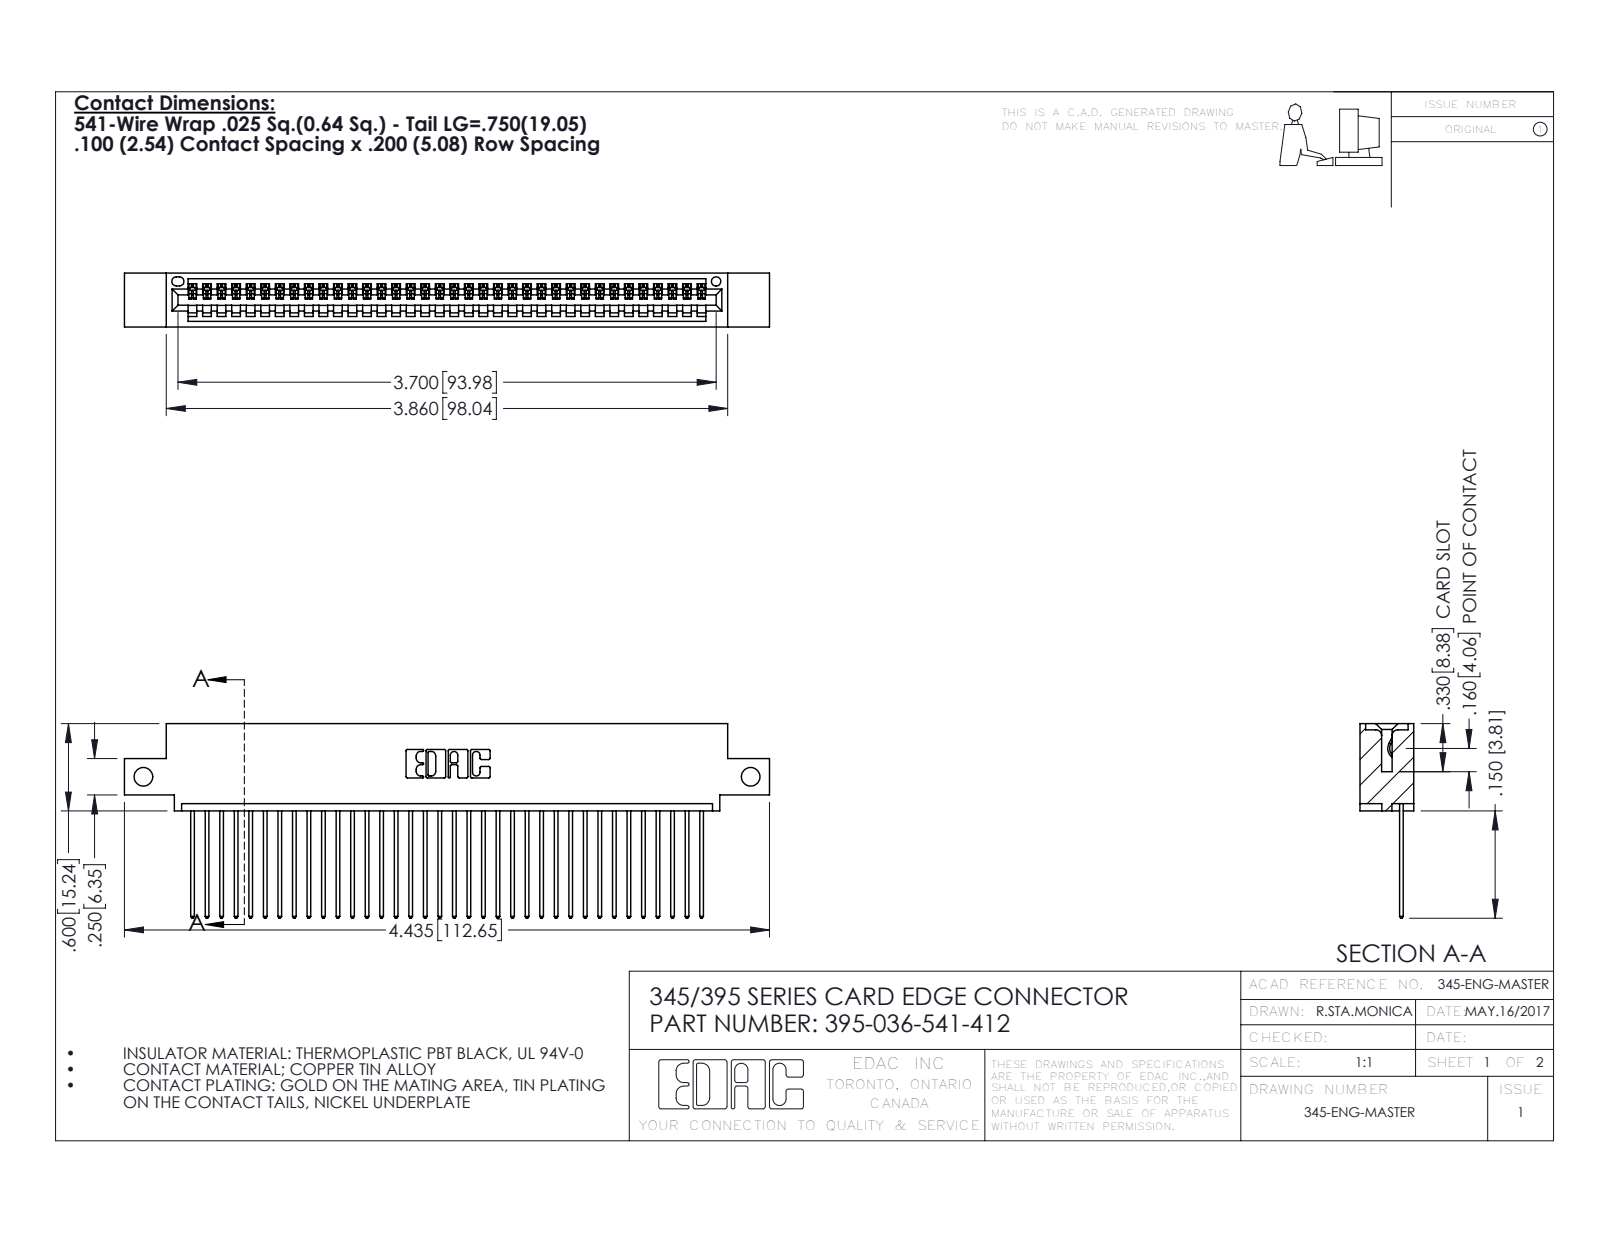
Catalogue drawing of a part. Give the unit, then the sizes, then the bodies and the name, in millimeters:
Units: millimetres
Overall size (bounding box): 112.6 × 34 × 9.4
Round holes (diameter × count): ⌀3.3 ×2, ⌀1.6 ×1
Partial cylindrical surfaces — rounded edges, fillets, slot ends (radius × count): R0.2 ×72, R0.3 ×72, R0.3 ×22, R0.2 ×6, R0.8 ×6, R0.7 ×3, R0.8 ×2, R1 ×2
Main face-to-face distances: 1.8, 7.6, 2.5, 6.9, 0.6, 9.4, 5.1, 5.7, 3.8, 1.8
Hole centre spacings: 106
Volume: 10 600 mm³ · Surface area: 14 660 mm²
Bodies: 37 solids, 2218 faces (1524 planar, 694 cylindrical, 0 other)
Part name (STEP PRODUCT): 345 Part_0.110 Offset - Side Mount; 395-036-541-412; 345-292-001_345-293-141
STEP written by: SolidWorks 2016 (CONFIG_CONTROL_DESIGN)
